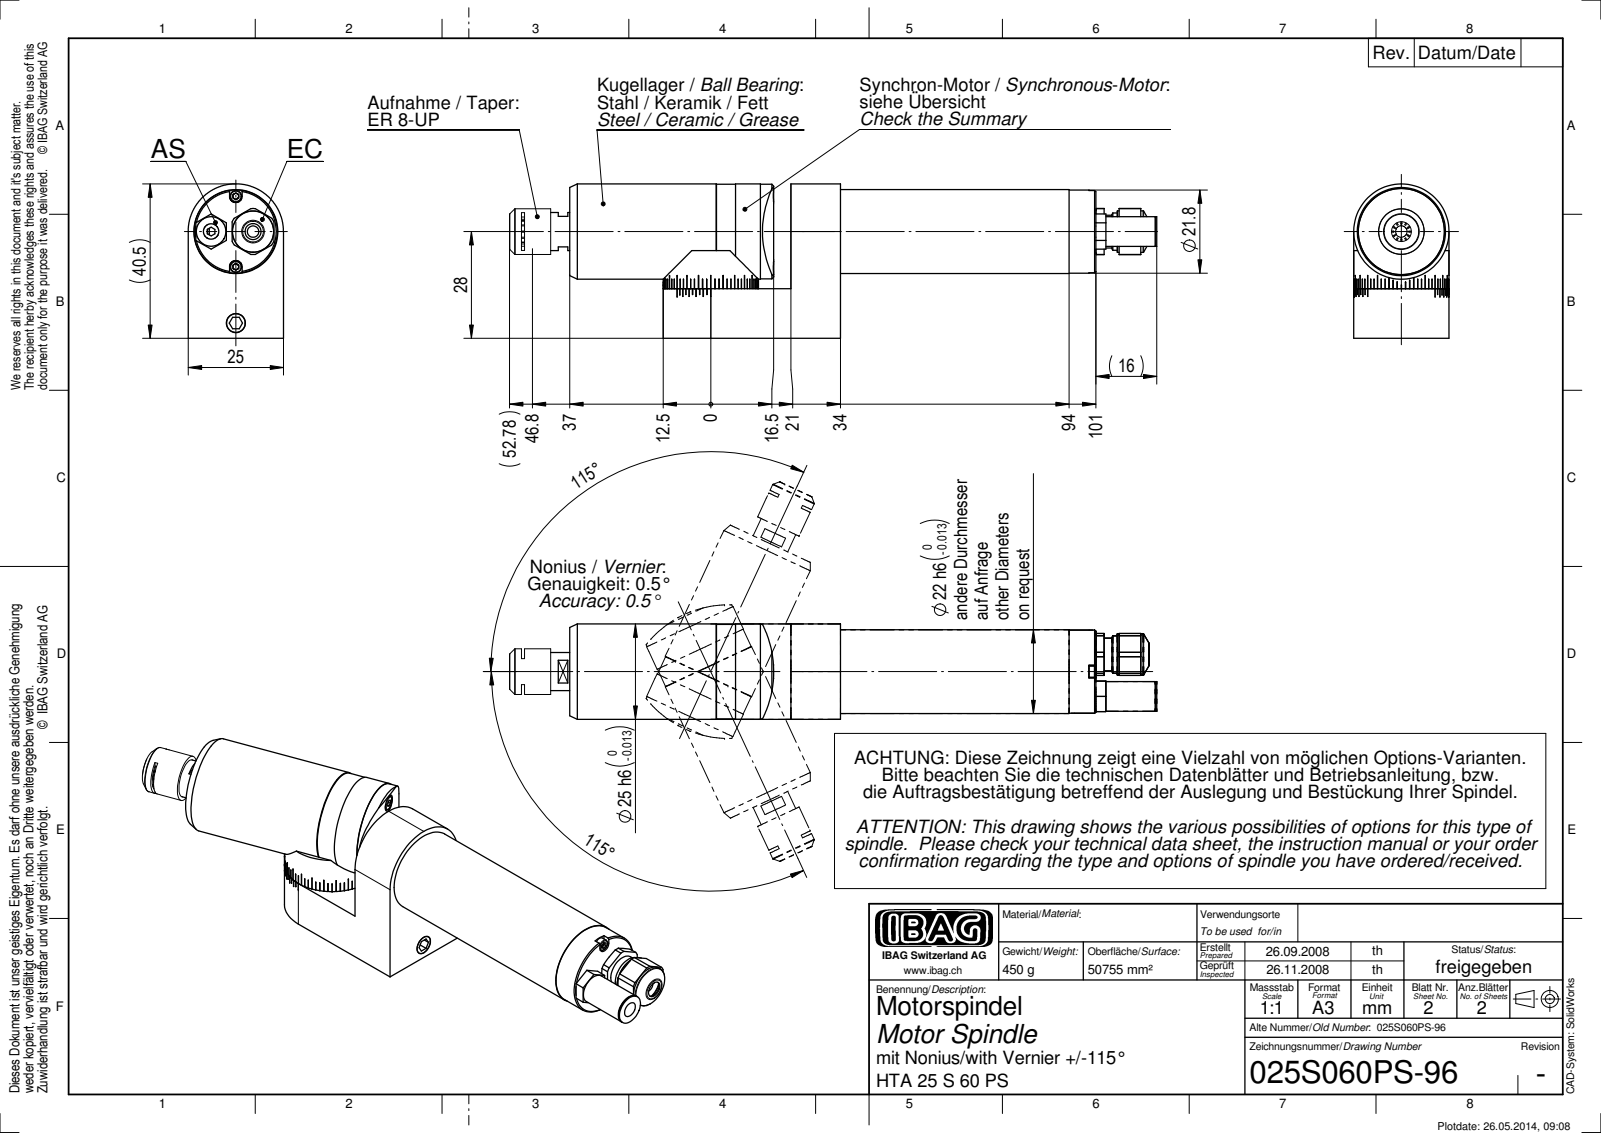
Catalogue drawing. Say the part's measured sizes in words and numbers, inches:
The part is named "025S060PS-96". Its 3-D file was written by "SolidWorks 2010 (CONFIG_CONTROL_DESIGN)". It is 0 solids with 276 faces: 127 planar, 109 cylindrical and 40 other. Overall it measures 6.684 by 1.594 by 0.984 inches. Round holes: 2 of diameter 0.118, 1 of diameter 0.157, 1 of diameter 0.165, 1 of diameter 0.173, 1 of diameter 0.197, 1 of diameter 0.205, 1 of diameter 0.36, 1 of diameter 0.417. Round bosses or shafts: 2 of diameter 0.984, 2 of diameter 0.118, 1 of diameter 0.976, 1 of diameter 0.866, 1 of diameter 0.858, 1 of diameter 0.472, 1 of diameter 0.429, 1 of diameter 0.394. Partial cylindrical surfaces (rounded edges, fillets, slot ends): 4 of radius 0.061, 4 of radius 0.114, 2 of radius 0.065, 1 of radius 0.167, 1 of radius 0.201, 1 of radius 0.238, 1 of radius 0.254, 1 of radius 0.376. The main face-to-face distances are 0.512, 0.984, 0.315, 2.283, 2.795, 2.724, 5.433, 3.15, 2.638, 1.969. The hole center spacings are 0.177, 0.256, 0.374, 0.414, 0.433, 0.453, 0.945, 0.961.
